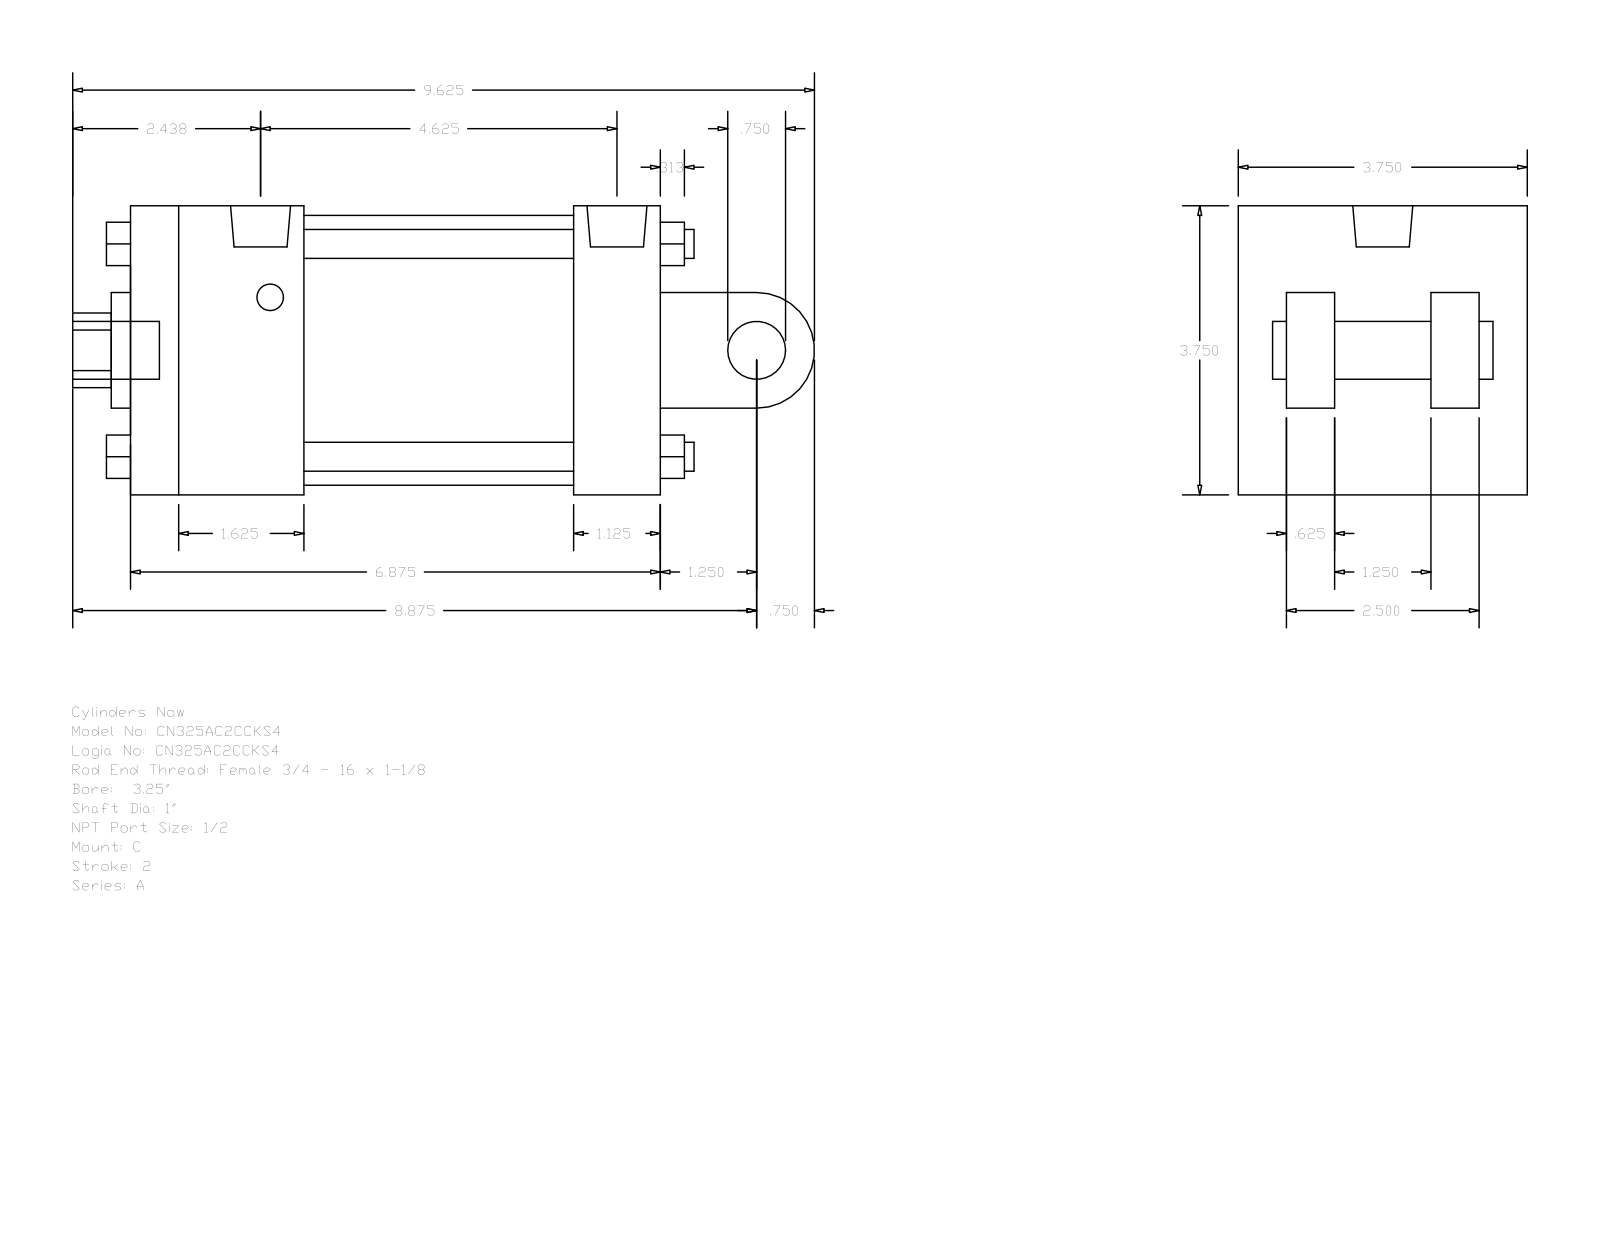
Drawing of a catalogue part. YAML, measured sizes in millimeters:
part_name: "A_C__0325_1"
step_written_by: "GSSL Pune (CONFIG_CONTROL_DESIGN)"
units: millimeters
bodies: {solids: 0, faces: 135, planar: 102, cylindrical: 33, other: 0}
overall_size: [244.47, 95.25, 95.25]
round_holes:
  - {diameter: 8.73, count: 2}
  - {diameter: 19.77, count: 1}
  - {diameter: 25.4, count: 1}
  - {diameter: 38.1, count: 1}
  - {diameter: 88.9, count: 1}
round_bosses_or_shafts:
  - {diameter: 9.53, count: 4}
  - {diameter: 19.05, count: 2}
  - {diameter: 8.73, count: 2}
  - {diameter: 19.77, count: 1}
partial_cylinders:
  - {radius: 12.29, count: 1}
  - {radius: 19.05, count: 1}
face_to_face_distances: [95.24, 174.63, 15.87, 63.5, 47.63, 79.37, 31.74, 66.67, 146.05, 28.58]
hole_center_spacings: [3.18]
